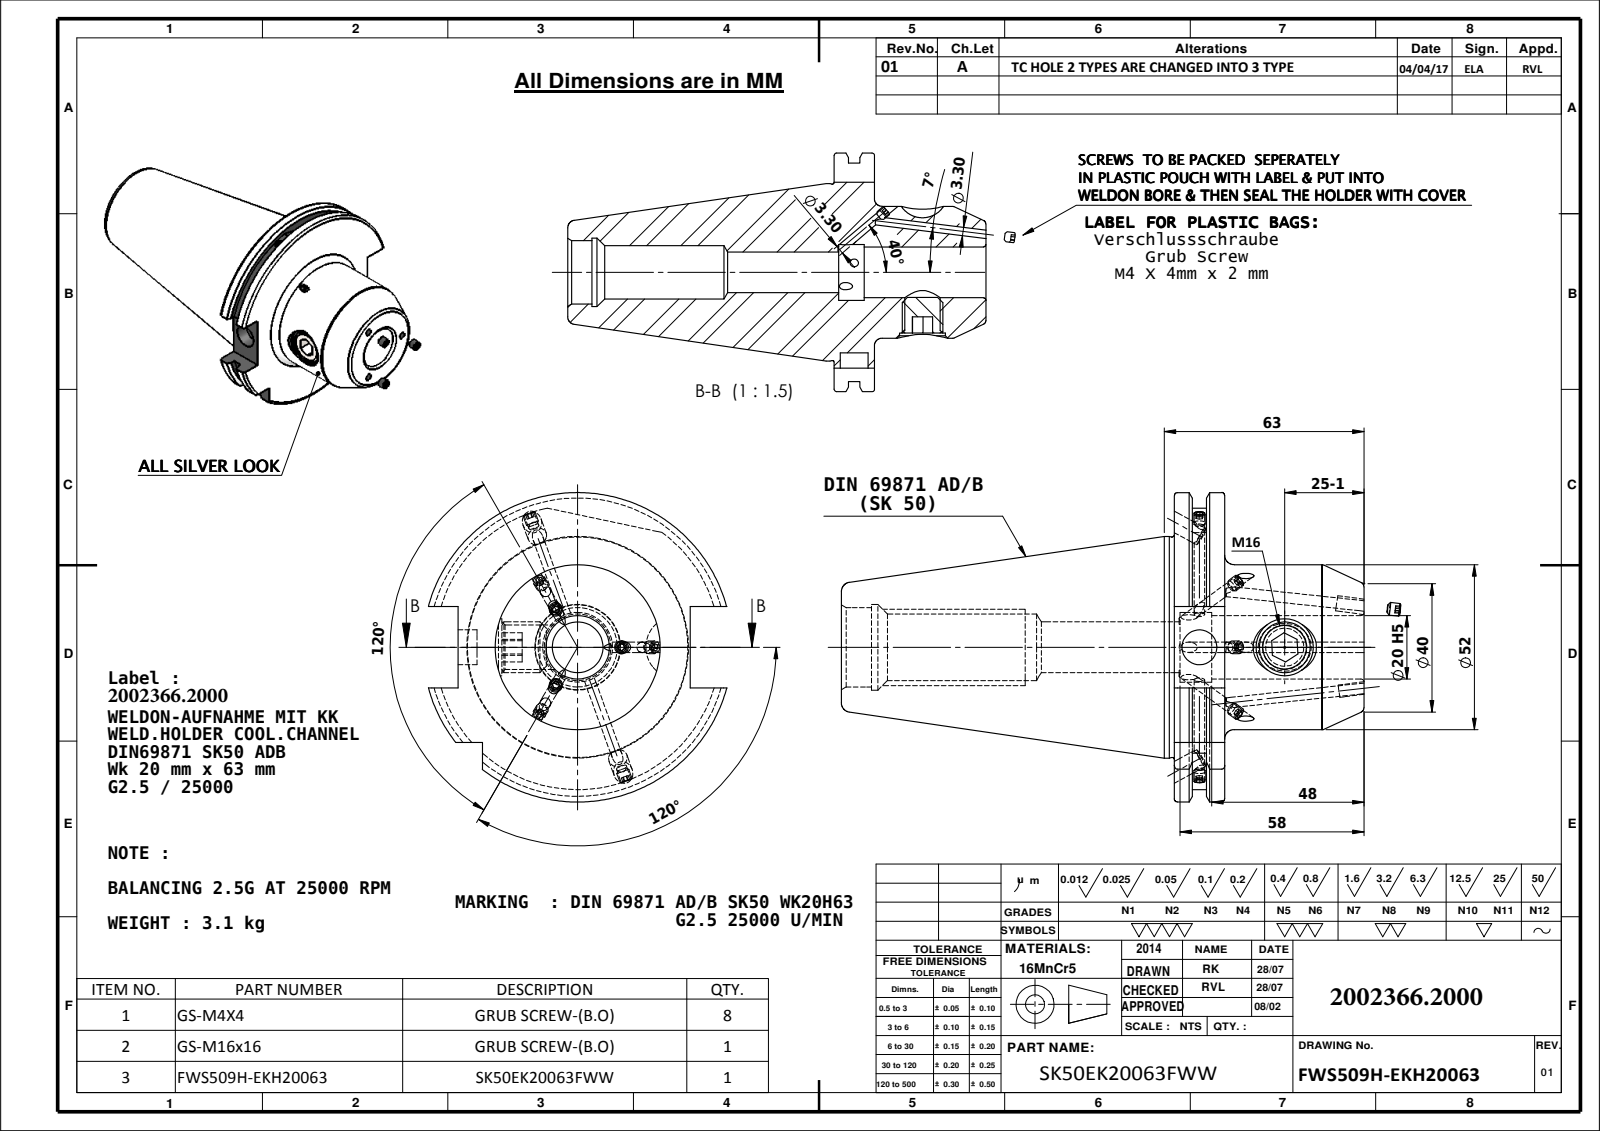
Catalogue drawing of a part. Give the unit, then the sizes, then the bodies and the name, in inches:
Units: inches
Overall size (bounding box): 7.187 × 3.839 × 3.703
Round holes (diameter × count): ⌀0.13 ×3, ⌀0.236 ×2, ⌀0.433 ×1, ⌀0.472 ×1, ⌀0.551 ×1, ⌀0.63 ×1, ⌀0.787 ×1, ⌀0.827 ×1, ⌀0.866 ×1, ⌀0.984 ×1, ⌀1.063 ×1
Round bosses / shafts (diameter × count): ⌀0.157 ×4, ⌀2.75 ×1, ⌀2.734 ×1, ⌀2.047 ×1
Partial cylindrical surfaces — rounded edges, fillets, slot ends (radius × count): R1.768 ×1, R1.919 ×1
Main face-to-face distances: 0.626, 2.354, 1.728, 0.4, 0.226, 1.955, 0.223, 0.177, 0.403, 2.131
Hole centre spacings: 1.059
Volume: 24.48 in³ · Surface area: 86.4 in²
Bodies: 6 solids, 202 faces (75 planar, 63 cylindrical, 64 other)
Part name (STEP PRODUCT): Copy of M4X4_DIN 913 - M4 x 4-N; M16X16_ISO 4026 - M16 x 10-N; SK50 EK 20 063 FTC WW
STEP written by: SolidWorks 2009 (CONFIG_CONTROL_DESIGN)
